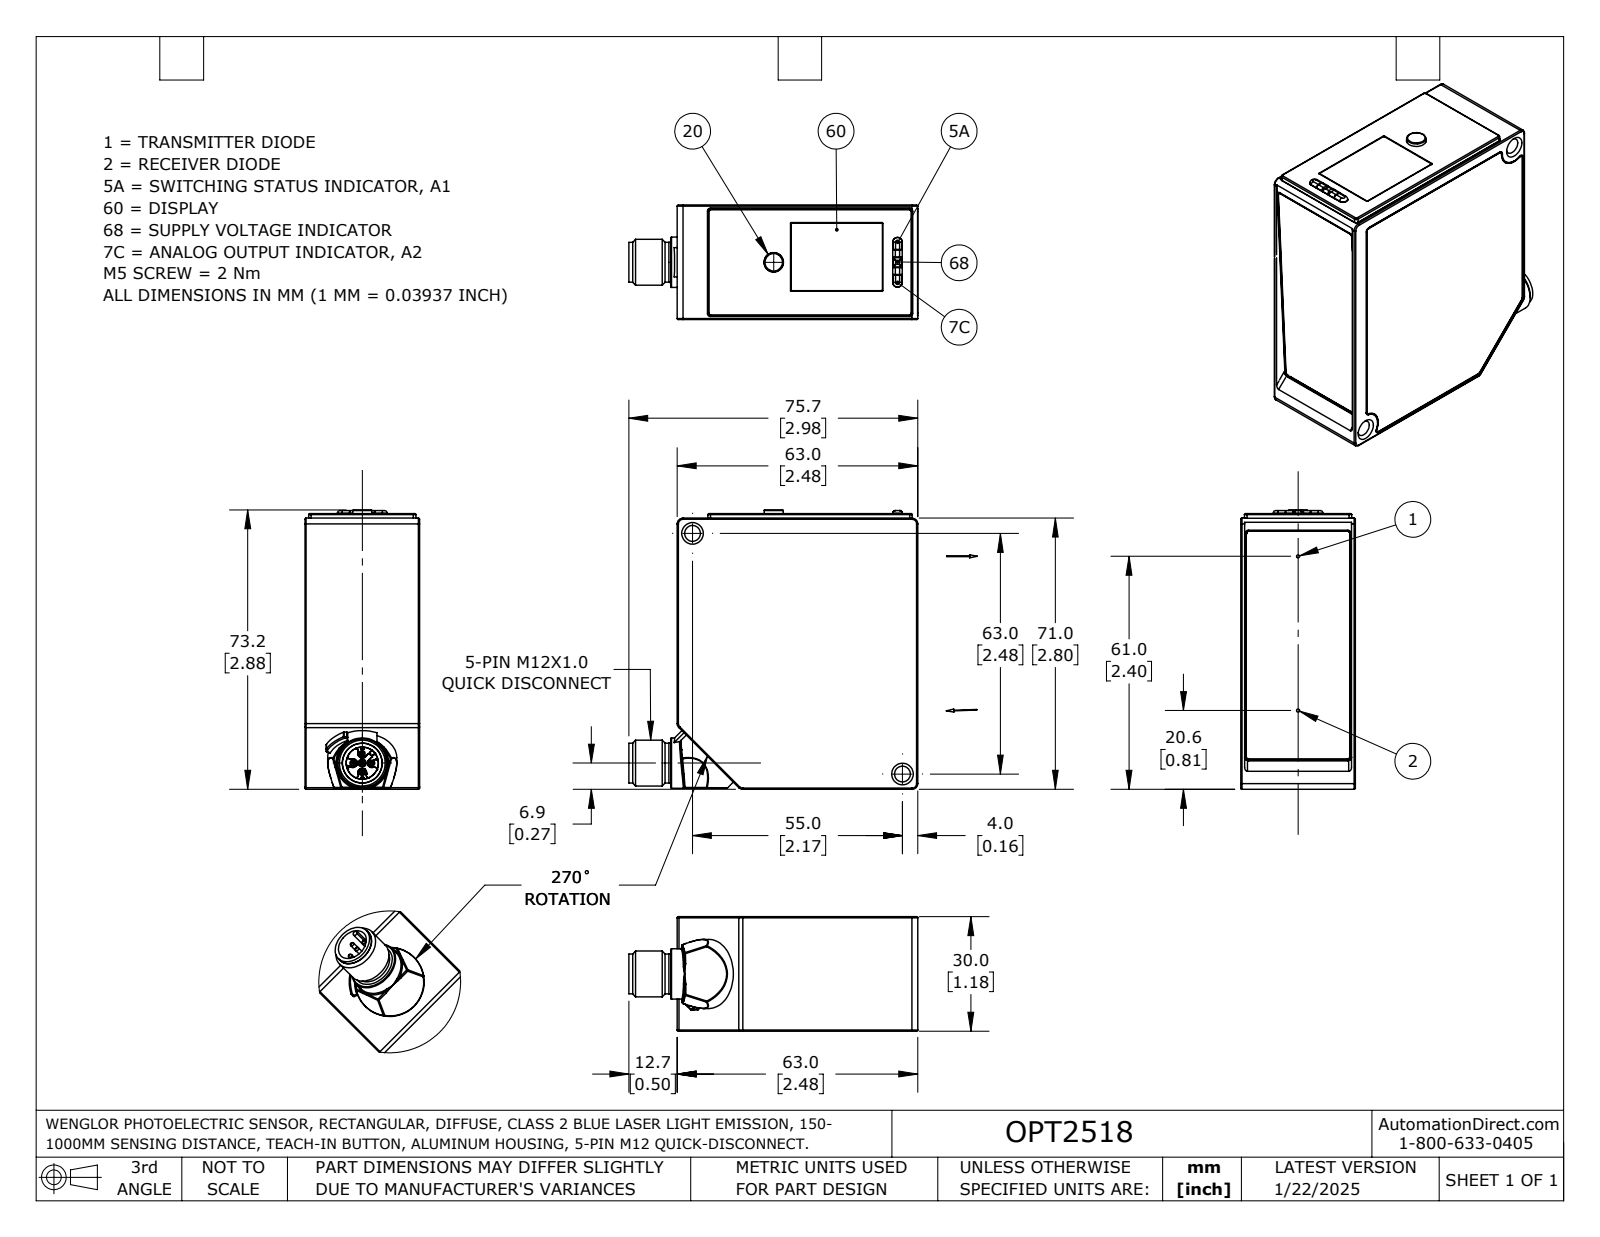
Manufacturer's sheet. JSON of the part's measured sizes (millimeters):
{"part_name": "OPT2517_OPT2518", "step_written_by": "SolidWorks 2024 (AUTOMOTIVE_DESIGN)", "units": "millimeters", "bodies": {"solids": 3, "faces": 393, "planar": 169, "cylindrical": 119, "other": 105}, "overall_size": [91.3, 73.2, 30], "volume_mm3": 130600, "surface_area_mm2": 18850, "round_holes": [[1.5, 5], [4.1, 2], [5.1, 1]], "round_bosses_or_shafts": [[1, 5], [0.2, 2], [18.1, 1], [13.2, 1], [12, 1], [10.4, 1], [5, 1], [2.1, 1]], "partial_cylinders_radius": [[0.3, 32], [0.7, 11], [0.2, 8], [0.7, 6], [0.8, 6], [1.5, 6], [0.7, 4], [0.8, 4]], "face_to_face_distances": [29.9, 72.2, 30, 1.2, 71, 1, 29, 63, 0.9, 70.7], "hole_center_spacings": [2.5, 3.5, 5, 83.6]}
